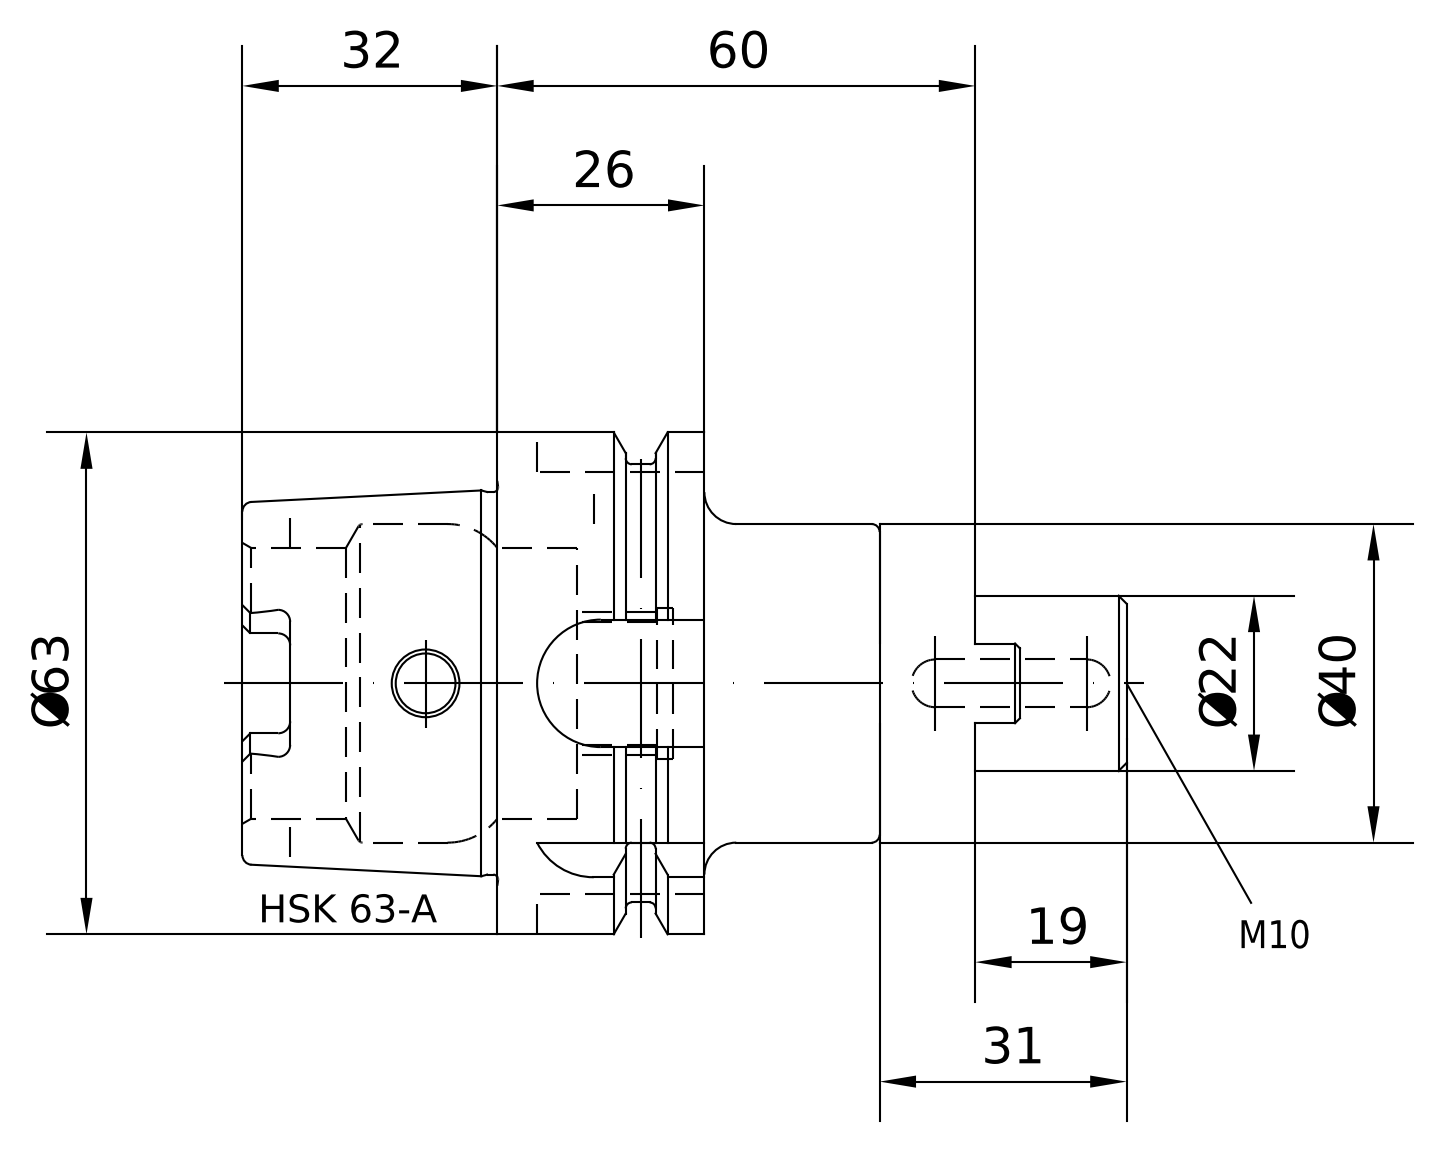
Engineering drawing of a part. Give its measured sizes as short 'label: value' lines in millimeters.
name: A63-040-22; 85-200-22; A63-040-22_ASM
written by: PRO/ENGINEER BY PARAMETRIC TECHNOLOGY CORPORATION, 2010430 (CONFIG_CONTROL_DESIGN)
unit: mm
bodies: 2 solids, 263 faces (123 planar, 64 cylindrical, 76 other)
size: 111 × 63 × 63
volume: 127 985 mm³; area: 34 570 mm²
holes: 2× ⌀10, 1× ⌀7.5, 1× ⌀8.5, 1× ⌀16.92, 1× ⌀18.32, 1× ⌀18.66, 1× ⌀22.36, 1× ⌀26, 1× ⌀34
bosses: 1× ⌀63, 1× ⌀55, 1× ⌀48.04, 1× ⌀40, 1× ⌀22, 1× ⌀18
rounds: 6× R1.5, 6× R3, 1× R5.05, 1× R8, 1× R8.02, 1× R9.02
face distances: 48, 22, 26, 10, 60, 34, 12, 16, 38, 50
